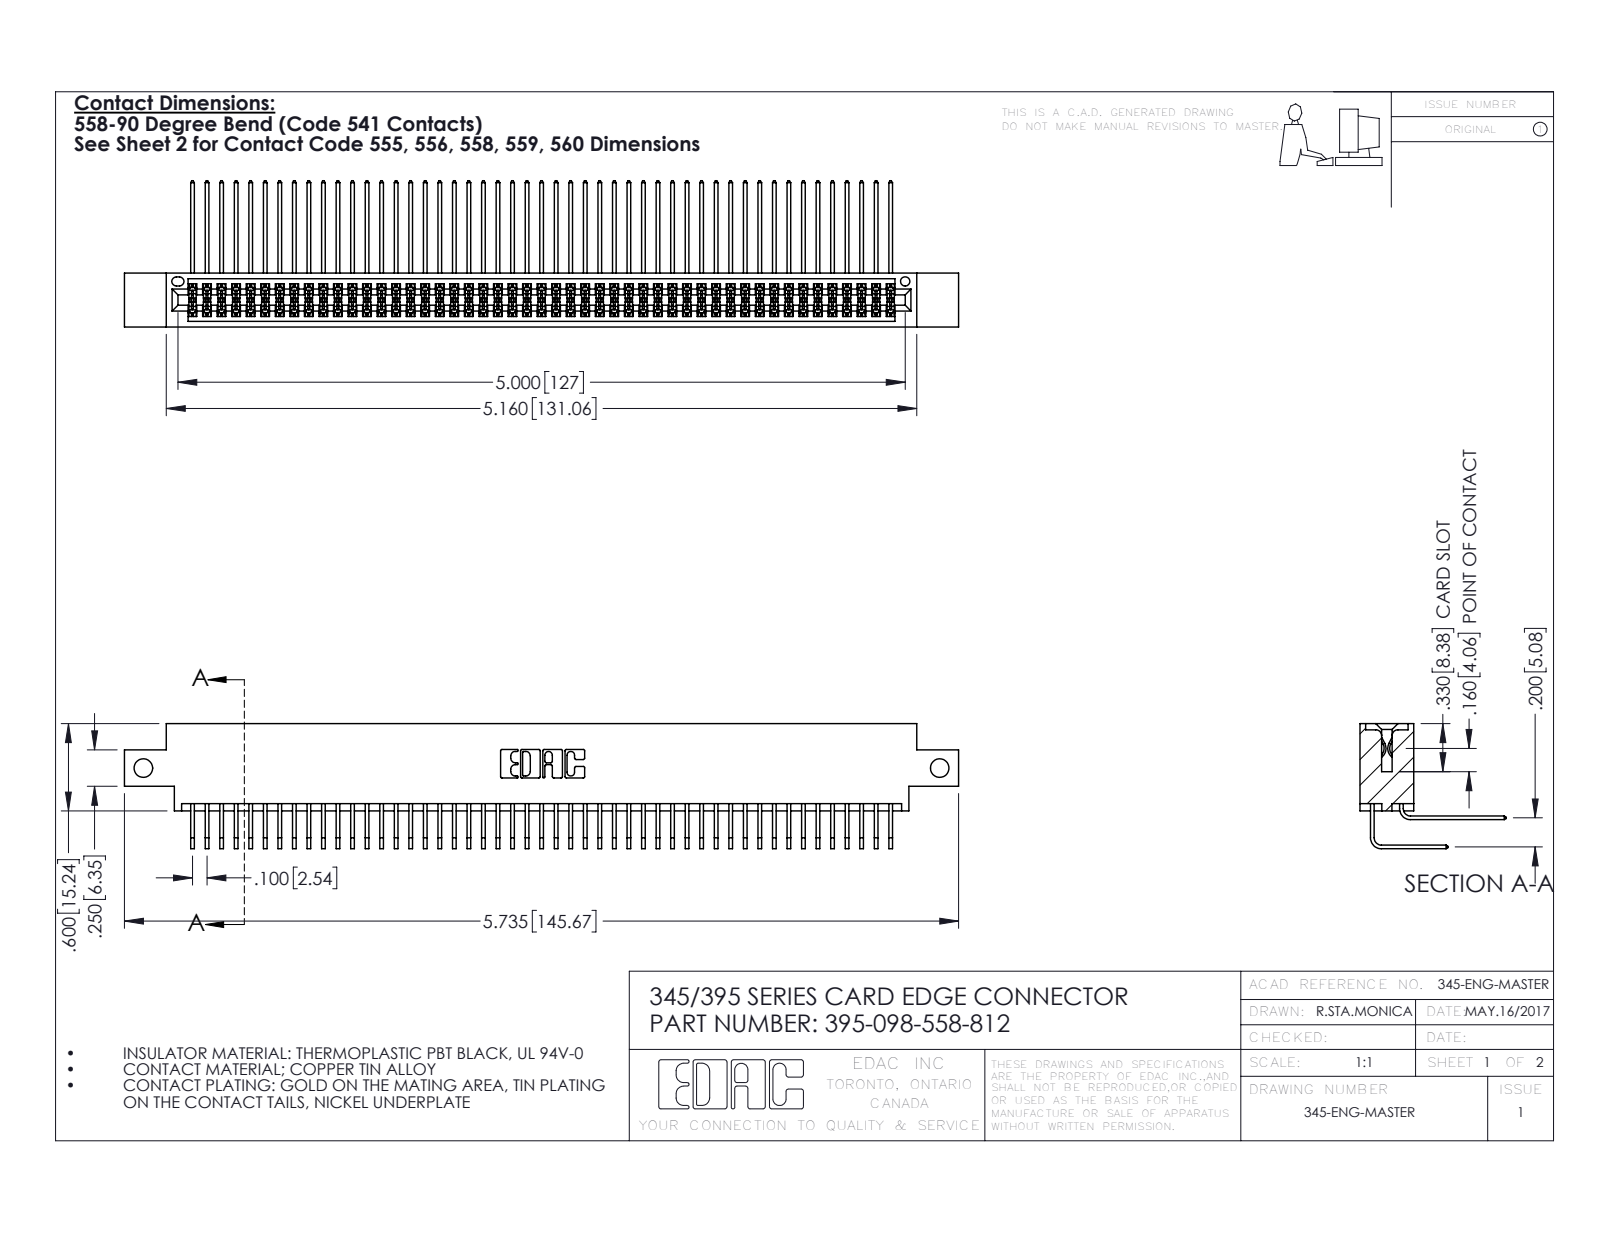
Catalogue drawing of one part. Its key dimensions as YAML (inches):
part_name: "345-292-001_558 559 Tail - 1; 395-098-558-812; 345-292-001_558 Tail - 2; 345 Part_0.170 Offset - Side Mount"
step_written_by: "SolidWorks 2016 (CONFIG_CONTROL_DESIGN)"
units: inches
bodies: {solids: 99, faces: 5226, planar: 3514, cylindrical: 1712, other: 0}
overall_size: [5.735, 1.005, 0.859]
volume: 0.89
surface_area: 37.75
round_holes:
  - {diameter: 0.128, count: 2}
  - {diameter: 0.064, count: 1}
partial_cylinders:
  - {radius: 0.006, count: 148}
  - {radius: 0.01, count: 22}
  - {radius: 0.007, count: 6}
  - {radius: 0.031, count: 6}
  - {radius: 0.026, count: 3}
  - {radius: 0.014, count: 2}
  - {radius: 0.019, count: 2}
  - {radius: 0.022, count: 2}
face_to_face_distances: [0.072, 0.298, 0.2, 0.37, 0.098, 0.272, 0.025, 0.225, 0.175, 0.025]
hole_center_spacings: [5.475]
